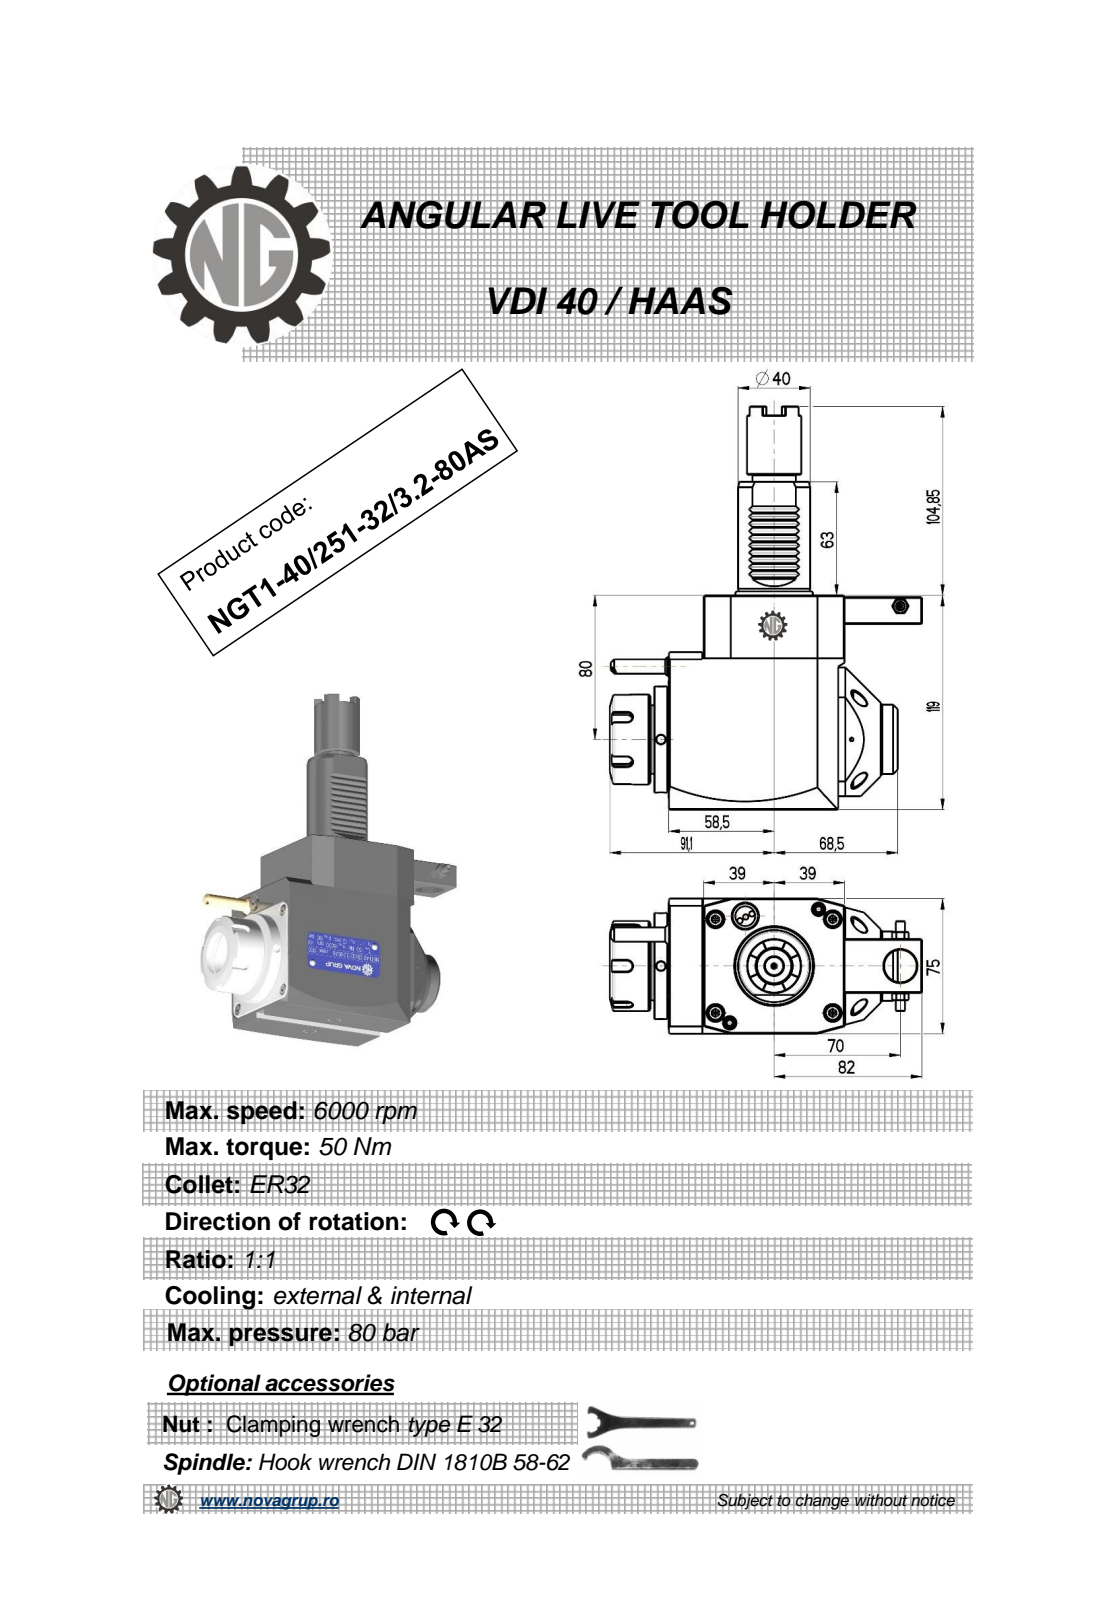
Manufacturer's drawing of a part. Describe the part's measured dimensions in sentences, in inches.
The part is named "NGT1_40_251_32_3_2_80AS". Its 3-D file was written by "PRO/ENGINEER BY PARAMETRIC TECHNOLOGY CORPORATION, 2010280 (CONFIG_CONTROL_DESIGN)". It is 1 solid with 484 faces: 239 planar, 99 cylindrical and 146 other. Overall it measures 8.813 by 6.815 by 2.953 inches. Its volume is 64.26 cubic inches and its surface area 133.3 square inches. Round holes: 3 of diameter 0.197, 1 of diameter 0.118, 1 of diameter 0.165, 1 of diameter 0.374, 1 of diameter 0.709, 1 of diameter 1.063, 1 of diameter 1.811. Round bosses or shafts: 1 of diameter 2.323, 1 of diameter 1.969, 1 of diameter 1.811, 1 of diameter 1.614, 1 of diameter 1.575, 1 of diameter 1.516, 1 of diameter 1.181, 1 of diameter 0.945. Partial cylindrical surfaces (rounded edges, fillets, slot ends): 12 of radius 0.01, 10 of radius 0.012, 6 of radius 0.008, 5 of radius 0.118, 2 of radius 0.228, 2 of radius 0.236, 2 of radius 23.622, 1 of radius 0.02. The main face-to-face distances are 2.953, 4.685, 0.768, 3.839, 3.071, 0.76, 3.831, 1.083, 0.039, 0.138. The hole center spacings are 1.436, 1.737, 2.854, 5.226, 5.983.
